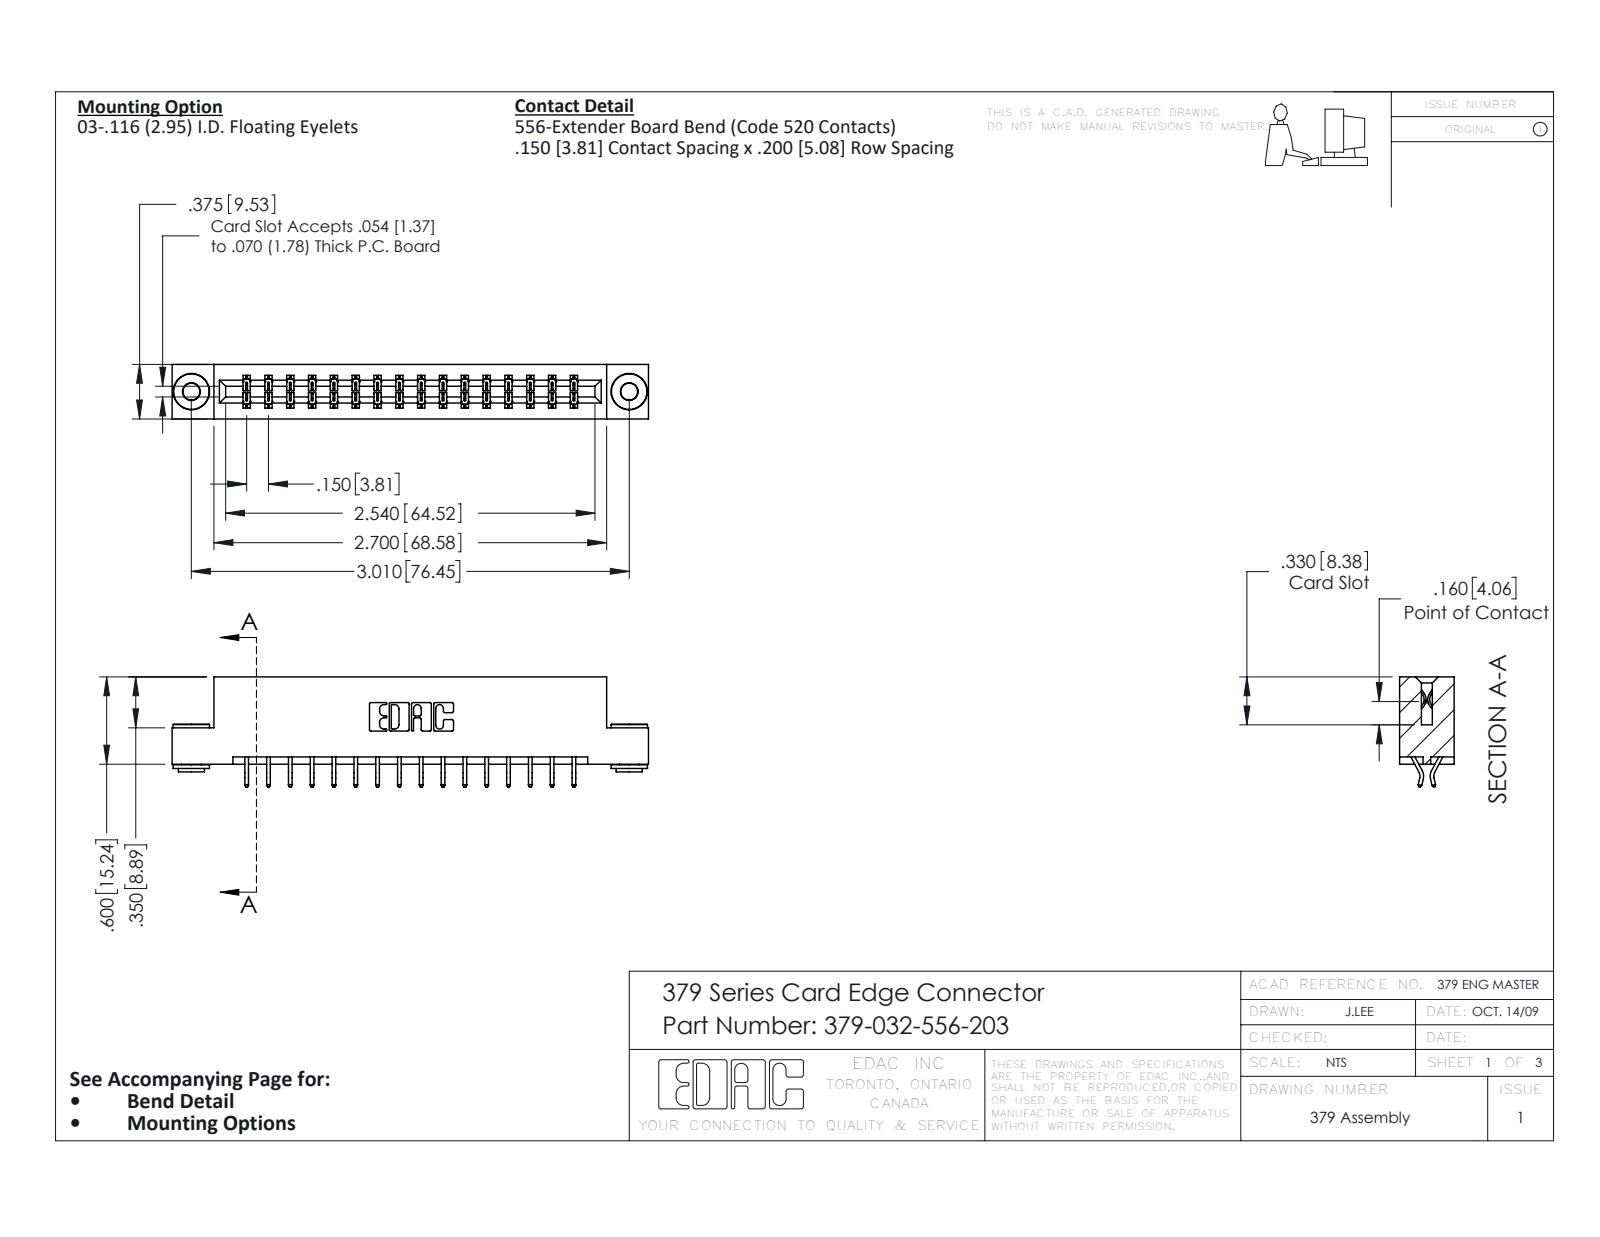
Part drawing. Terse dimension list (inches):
name: 379 Part_Flush - .156 Dia - TH; 379-032-556-203; 345-250-002_345-250-002-102; 345-292-001_556 Tail
written by: SolidWorks 2020 (CONFIG_CONTROL_DESIGN)
unit: in
bodies: 35 solids, 2008 faces (1360 planar, 640 cylindrical, 8 other)
size: 3.275 × 0.757 × 0.375
volume: 0.522 in³; area: 14.82 in²
holes: 2× ⌀0.116, 2× ⌀0.156
bosses: 2× ⌀0.25, 2× ⌀0.18, 2× ⌀0.136
rounds: 48× R0.006, 22× R0.01, 6× R0.007, 6× R0.031, 3× R0.026, 2× R0.01, 2× R0.014, 2× R0.022
face distances: 0.3, 0.375, 0.075, 0.2, 0.1, 0.15, 0.05, 0.6, 0.225, 0.55
hole spacings: 3.01
